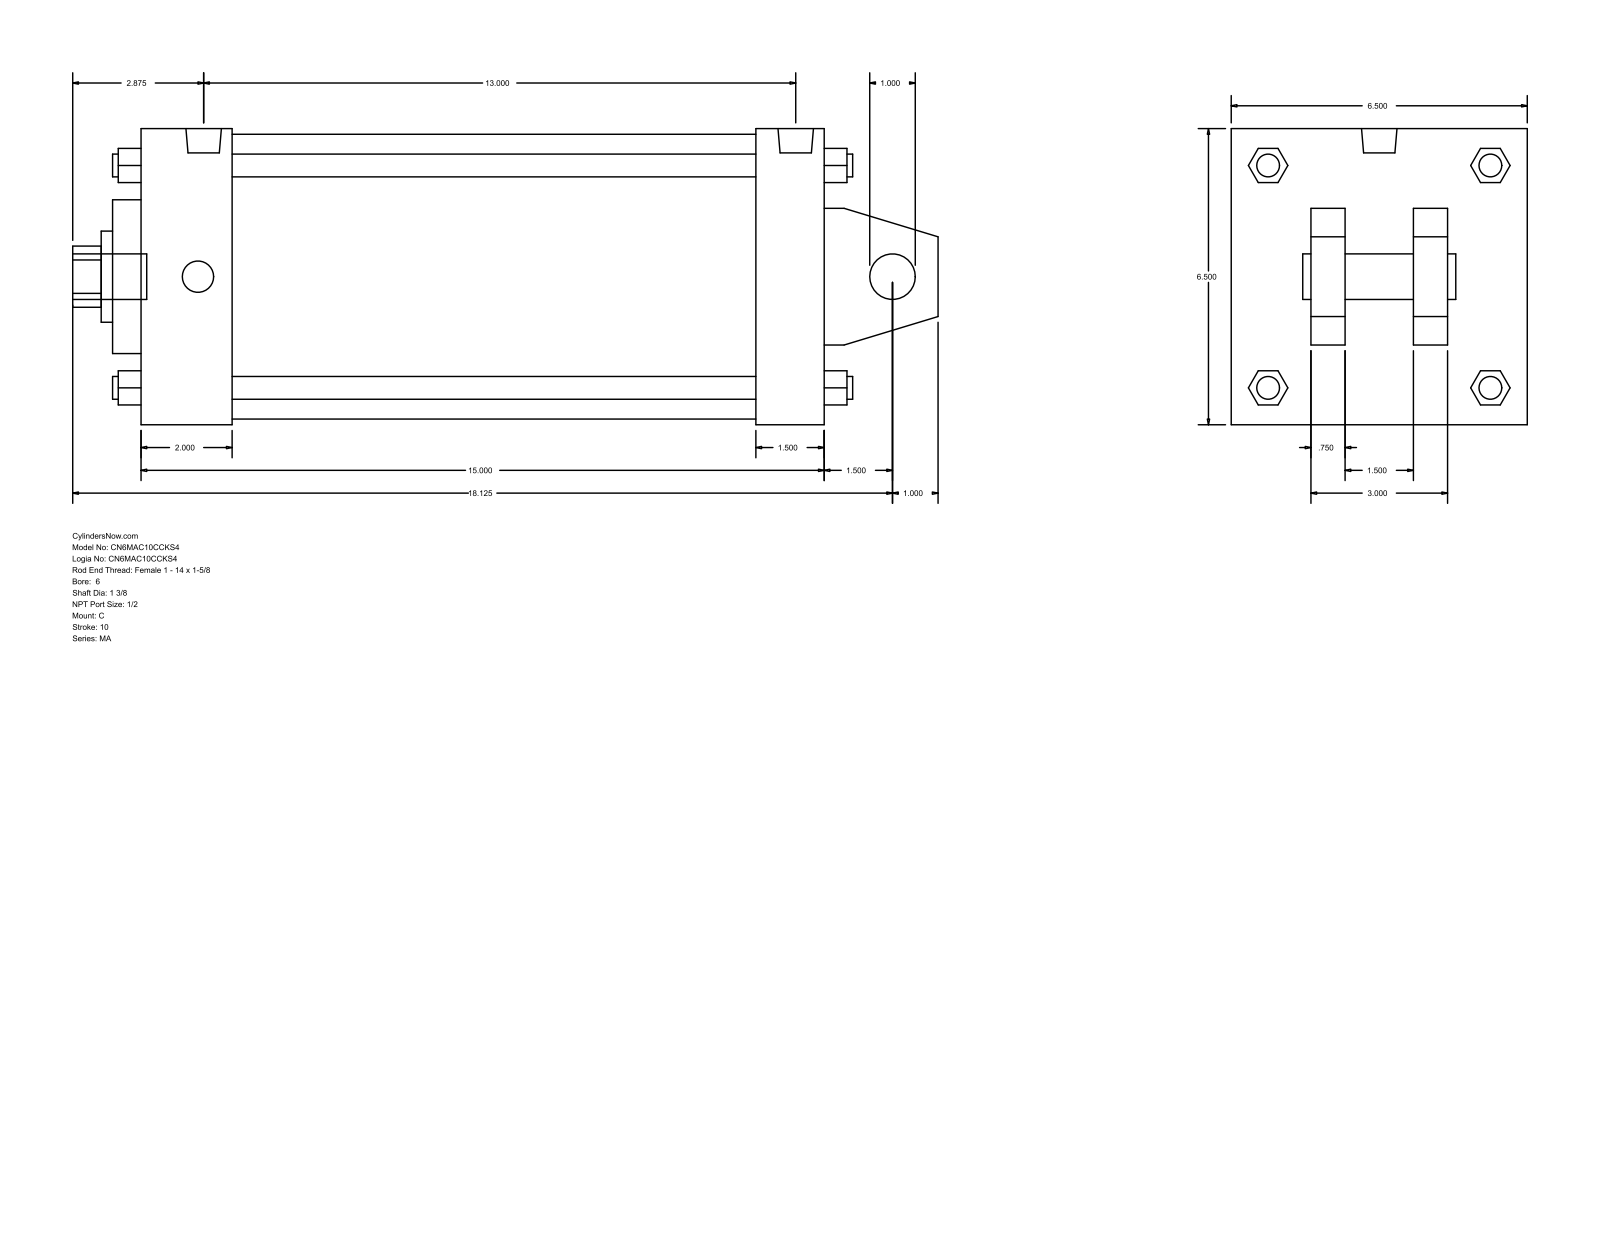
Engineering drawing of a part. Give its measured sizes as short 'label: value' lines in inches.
name: MA_C__0600_1.375
written by: GSSL Pune (CONFIG_CONTROL_DESIGN)
unit: in
bodies: 0 solids, 141 faces (109 planar, 32 cylindrical, 0 other)
size: 19 × 6.5 × 6.5
holes: 1× ⌀1, 1× ⌀1.375, 1× ⌀2, 1× ⌀3.375, 1× ⌀6.25
bosses: 4× ⌀0.687, 4× ⌀0.5, 2× ⌀0.778, 1× ⌀1
rounds: 1× R0.672
face distances: 6.5, 15, 1.5, 0.75, 2.5, 4, 2, 1.75, 4.75, 13.5
